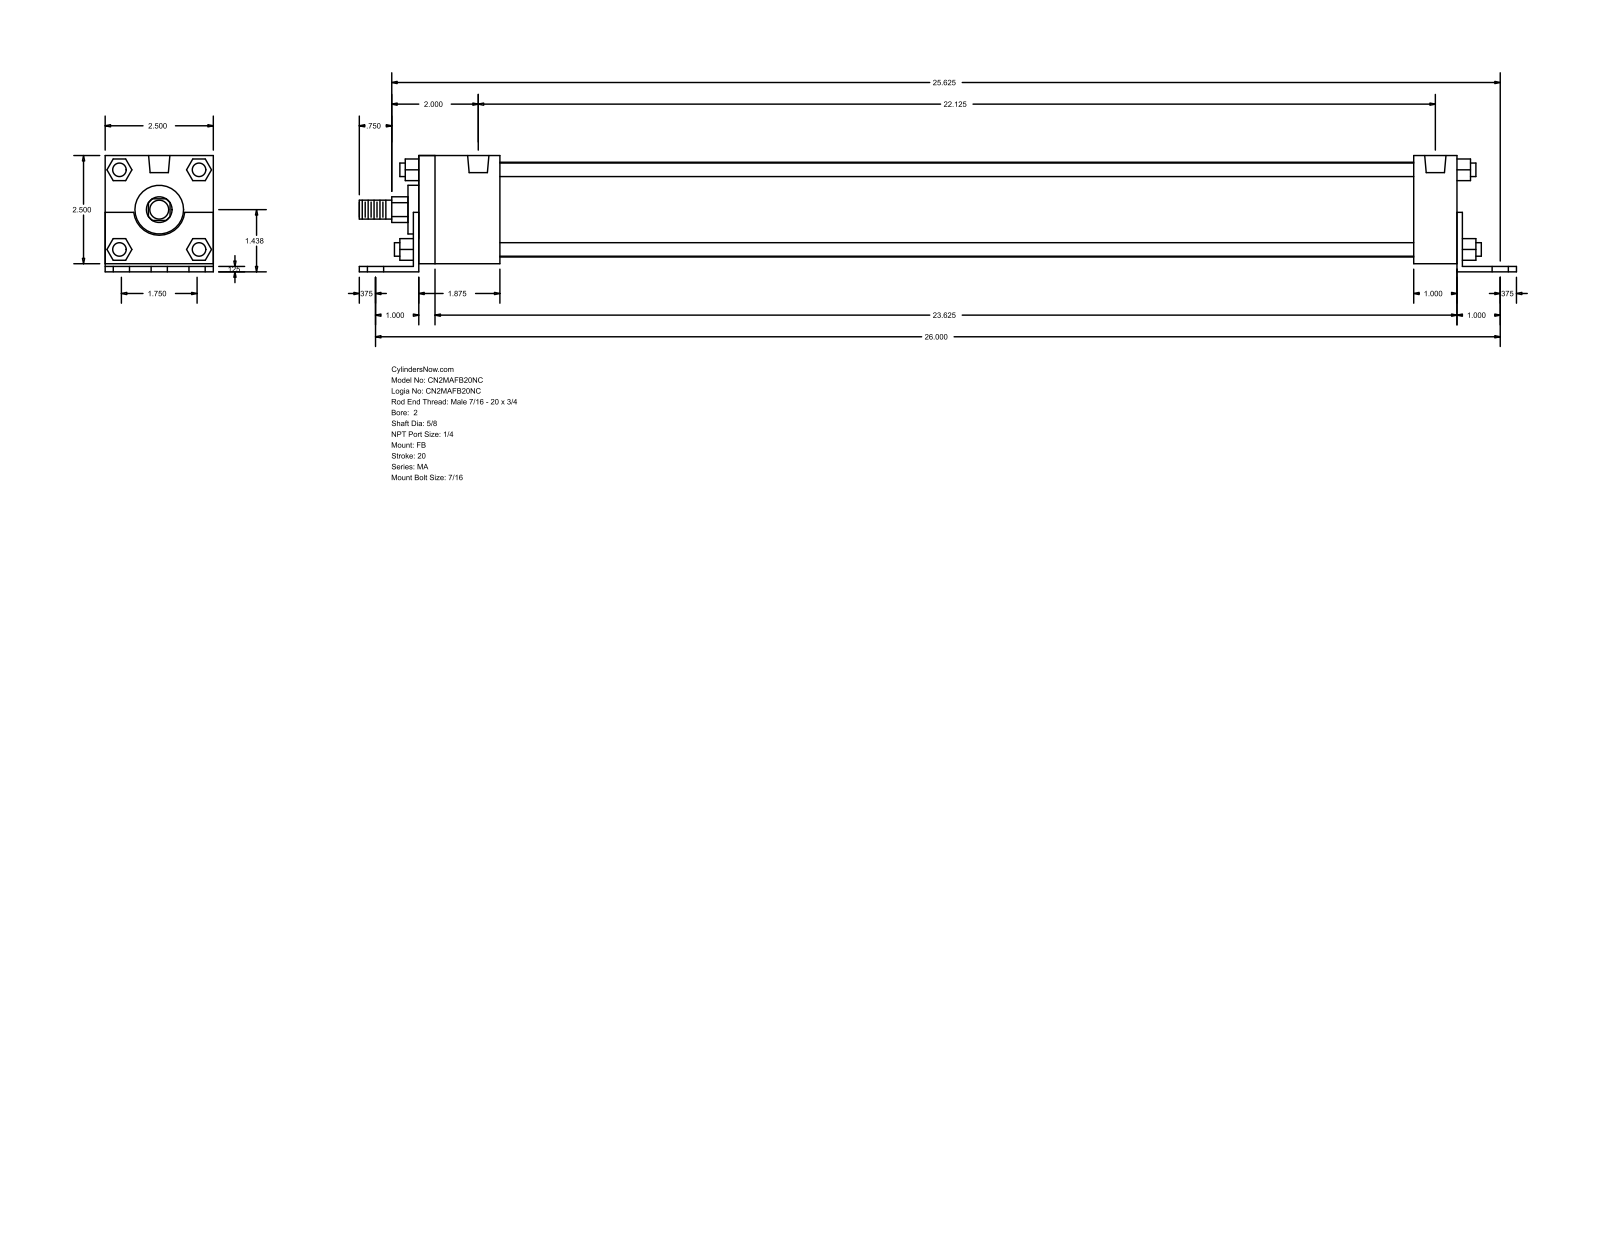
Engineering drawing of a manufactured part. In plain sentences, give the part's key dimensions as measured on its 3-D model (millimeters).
The part is named "MA_FB__0200_0.625". Its 3-D file was written by "GSSL Pune (CONFIG_CONTROL_DESIGN)". It is 0 solids with 140 faces: 105 planar, 35 cylindrical and 0 other. Overall it measures 679.45 by 68.26 by 63.5 millimeters. Round holes: 6 of diameter 11.11, 4 of diameter 7.94, 2 of diameter 12.49. Round bosses or shafts: 4 of diameter 7.94, 1 of diameter 55.63, 1 of diameter 28.57, 1 of diameter 15.88, 1 of diameter 11.11. Partial cylindrical surfaces (rounded edges, fillets, slot ends): 1 of radius 7.54, 1 of radius 15.05. The main face-to-face distances are 63.5, 3.17, 4.76, 68.26, 1.59, 65.09, 615.95, 3.18, 609.6, 612.77. The hole center spacings are 22.23, 660.78, 660.41, 44.12, 44.46, 64.3, 561.97, 600.49.
